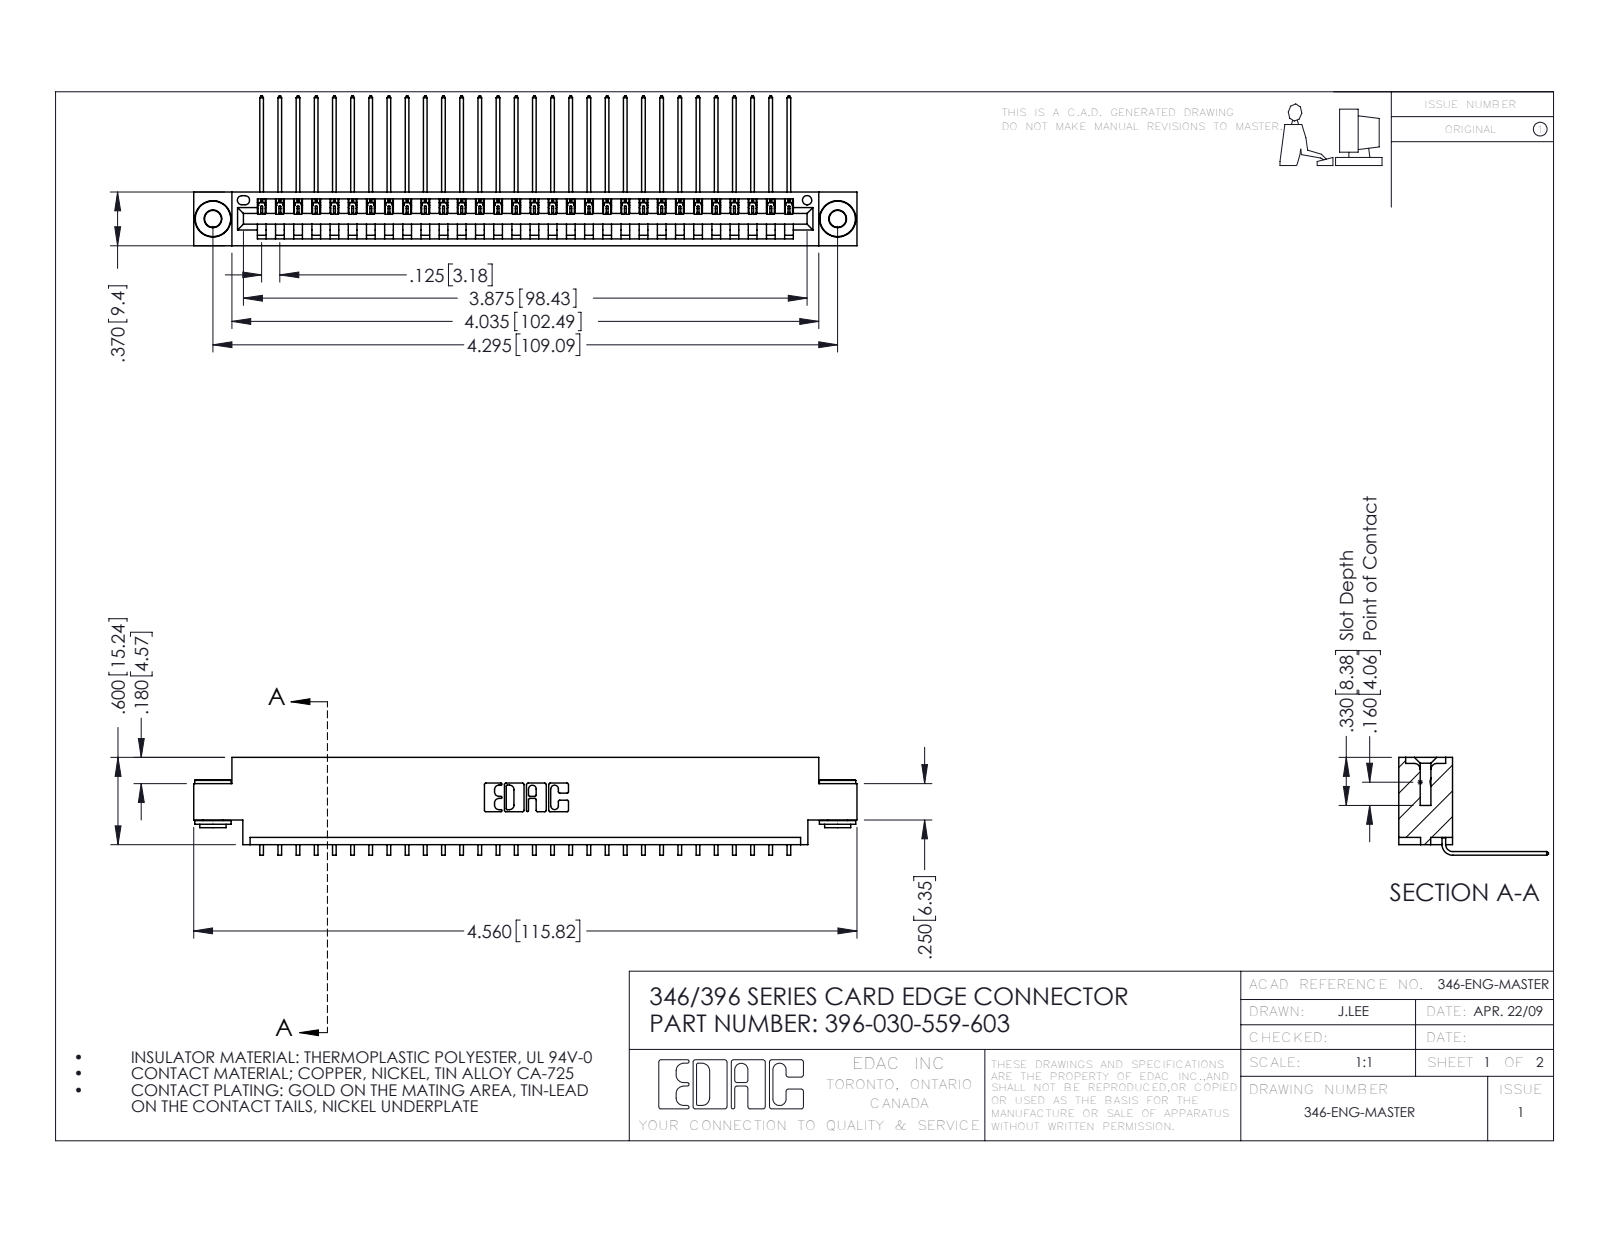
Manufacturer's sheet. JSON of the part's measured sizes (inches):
{"part_name": "345-292-001_558 559 Tail - 1; 346 Part_0.170 Offset - 0.156 Dia-TH; 396-030-559-603; 345-250-002_345-250-002-102", "step_written_by": "SolidWorks 2016 (CONFIG_CONTROL_DESIGN)", "units": "inches", "bodies": {"solids": 33, "faces": 1964, "planar": 1350, "cylindrical": 606, "other": 8}, "overall_size": [4.56, 1.03, 0.673], "volume_in3": 0.669, "surface_area_in2": 22.56, "round_holes": [[0.116, 2], [0.156, 2], [0.064, 1]], "round_bosses_or_shafts": [[0.25, 2], [0.18, 2], [0.136, 2]], "partial_cylinders_radius": [[0.006, 60], [0.01, 22], [0.007, 6], [0.031, 6], [0.026, 3], [0.031, 2], [0.04, 2], [0.014, 1]], "face_to_face_distances": [0.048, 0.322, 0.37, 0.25, 0.025, 0.072, 0.148, 0.222, 0.1, 0.174], "hole_center_spacings": [0.246, 4.087, 4.295]}
